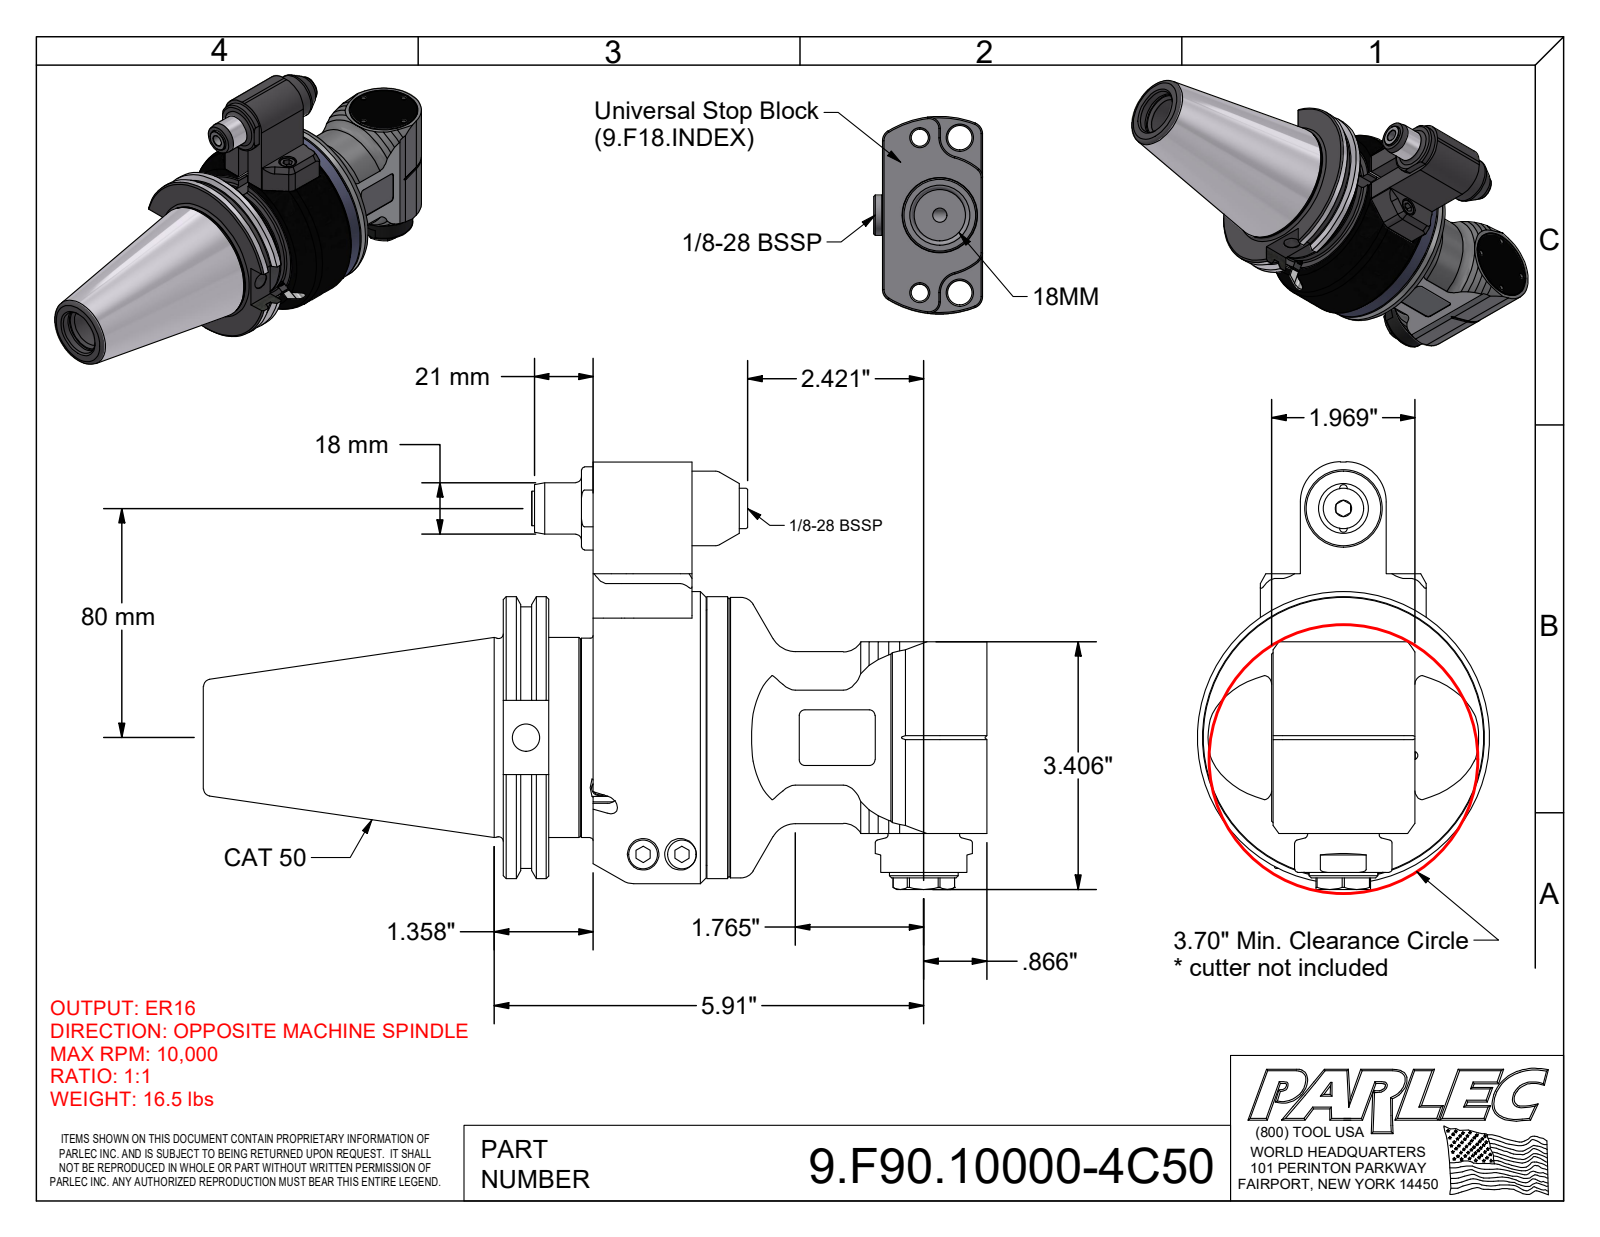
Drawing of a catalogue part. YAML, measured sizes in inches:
part_name: "9.F90.10000-4C50; 9.F90.10000; 9_GA1_458_2_4_C50; 9FL1ATC (+4 more)"
step_written_by: "Autodesk Inventor 2022 (AUTOMOTIVE_DESIGN)"
units: inches
bodies: {solids: 5, faces: 538, planar: 232, cylindrical: 142, other: 164}
overall_size: [10.772, 5.876, 4.016]
volume: 67.63
surface_area: 248.5
round_holes:
  - {diameter: 0.335, count: 20}
  - {diameter: 0.126, count: 4}
  - {diameter: 0.433, count: 3}
  - {diameter: 0.102, count: 2}
  - {diameter: 0.197, count: 2}
  - {diameter: 0.409, count: 2}
  - {diameter: 0.098, count: 1}
  - {diameter: 0.118, count: 1}
  - {diameter: 0.256, count: 1}
  - {diameter: 0.276, count: 1}
  - {diameter: 0.375, count: 1}
  - {diameter: 0.472, count: 1}
round_bosses_or_shafts:
  - {diameter: 0.236, count: 6}
  - {diameter: 0.394, count: 4}
  - {diameter: 0.709, count: 2}
  - {diameter: 0.315, count: 2}
  - {diameter: 0.098, count: 2}
  - {diameter: 4.016, count: 1}
  - {diameter: 3.875, count: 1}
  - {diameter: 3.874, count: 1}
partial_cylinders:
  - {radius: 0.079, count: 12}
  - {radius: 0.157, count: 4}
  - {radius: 0.016, count: 2}
  - {radius: 0.02, count: 2}
  - {radius: 0.039, count: 2}
  - {radius: 0.138, count: 2}
  - {radius: 0.197, count: 2}
  - {radius: 0.551, count: 2}
face_to_face_distances: [1.26, 0.904, 2.163, 1.555, 0.625, 1.528, 2.788, 0.335, 1.233, 0.608]
hole_center_spacings: [1.516, 2.144, 1.824, 3.002, 0.835, 2.651, 2.914, 3.031]
